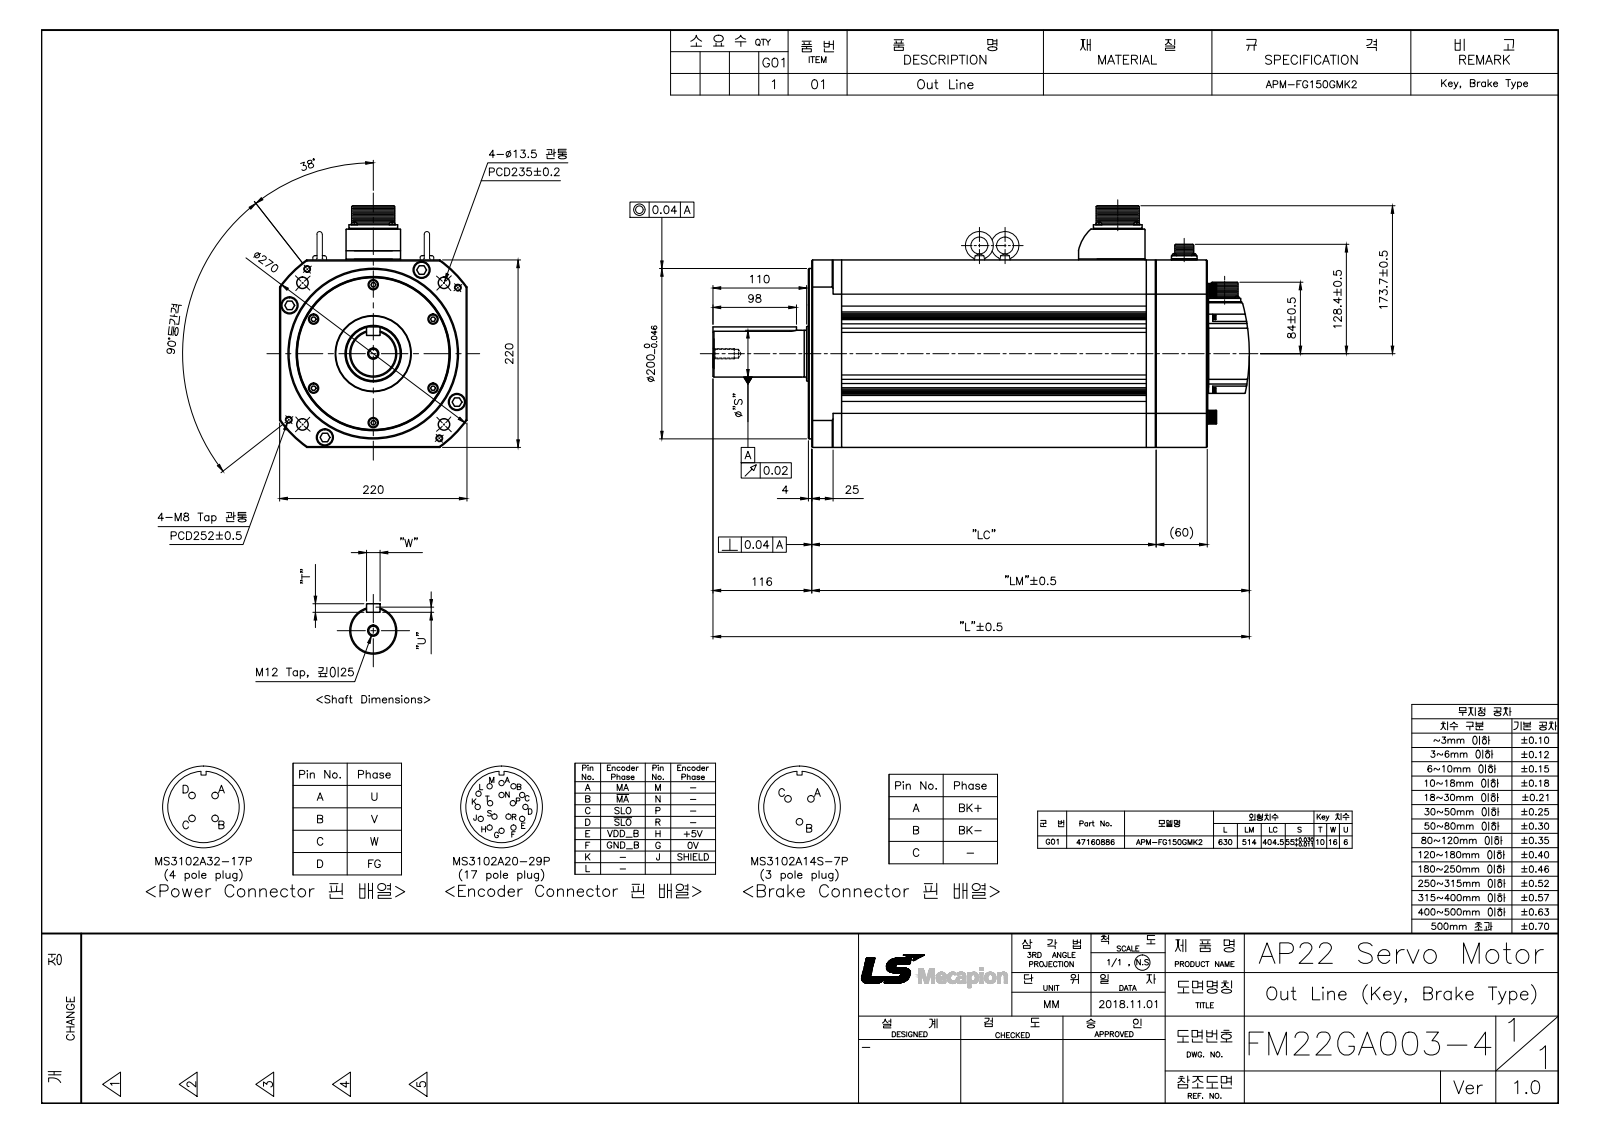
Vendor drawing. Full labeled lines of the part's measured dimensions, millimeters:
Part name (STEP PRODUCT): FM22GA003-4_Out Line(APM-FG150G_K2)
STEP written by: SolidWorks 2011 (AUTOMOTIVE_DESIGN)
Units: millimetres
Bodies: 82 solids, 2557 faces (923 planar, 1008 cylindrical, 626 other)
Overall size (bounding box): 630 × 283.7 × 220
Volume: 20 230 000 mm³ · Surface area: 1 174 000 mm²
Round holes (diameter × count): ⌀2.5 ×12, ⌀3 ×12, ⌀3.05 ×10, ⌀6.8 ×10, ⌀12 ×10, ⌀8 ×8, ⌀13.5 ×8, ⌀20 ×8, ⌀5 ×6, ⌀6 ×6, ⌀7 ×6, ⌀10.2 ×5
Round bosses / shafts (diameter × count): ⌀1.6 ×20, ⌀10 ×9, ⌀5.4 ×8, ⌀10.2 ×6, ⌀18 ×4, ⌀7 ×4, ⌀6 ×4, ⌀5.5 ×4
Partial cylindrical surfaces — rounded edges, fillets, slot ends (radius × count): R1 ×112, R2 ×17, R5 ×16, R4.5 ×12, R0.5 ×8, R2.5 ×4, R4 ×4, R6 ×4
Main face-to-face distances: 11.5, 40, 369.5, 358, 220, 180, 140, 14, 5, 21
Hole centre spacings: 81, 43.49, 118.14, 140.3, 161.32, 16.26, 17.11, 20.79
